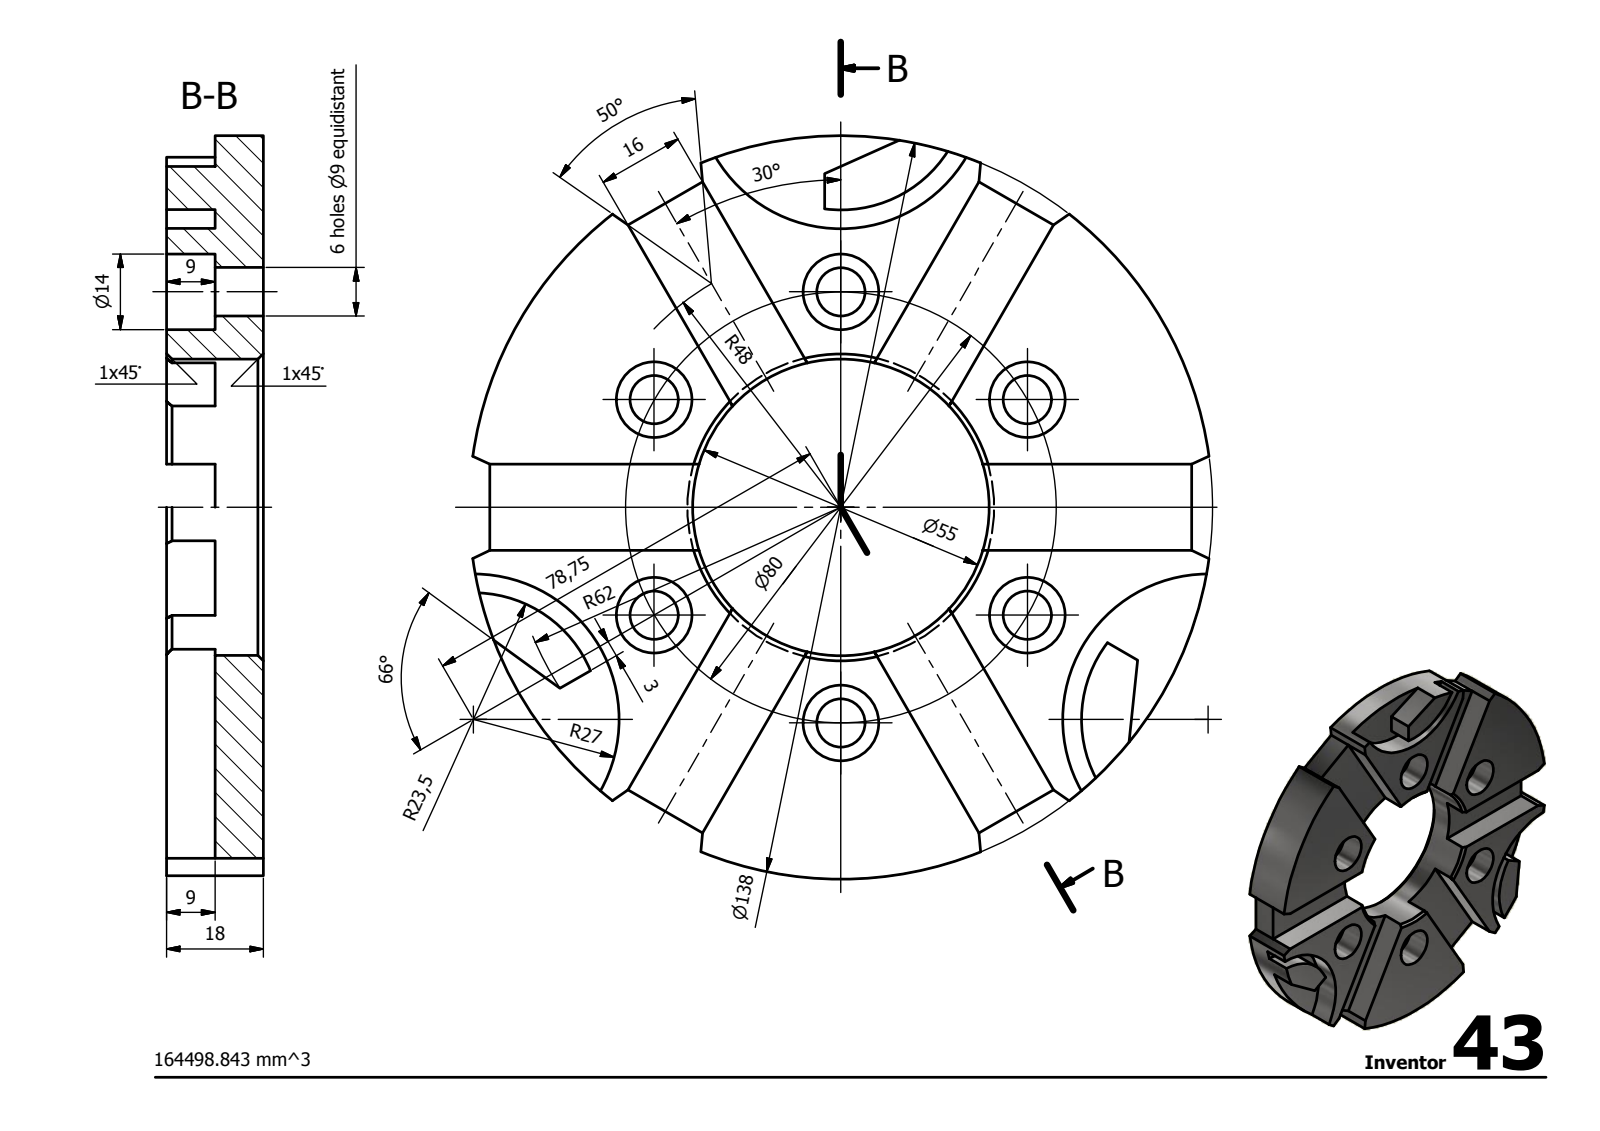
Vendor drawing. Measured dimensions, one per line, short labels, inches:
written by: Autodesk Inventor 2014 (AUTOMOTIVE_DESIGN)
unit: in
bodies: 1 solid, 93 faces (61 planar, 25 cylindrical, 7 other)
size: 5.433 × 5.381 × 0.709
volume: 10.04 in³; area: 66.6 in²
holes: 6× ⌀0.354, 6× ⌀0.551, 1× ⌀2.165
rounds: 3× R0.925, 3× R1.063, 1× R2.717
face distances: 0.354, 0.709, 0.63, 5.13, 5.131, 1.598, 1.599, 1.595, 2.683, 2.447
hole spacings: 1.575, 2.728, 3.15
